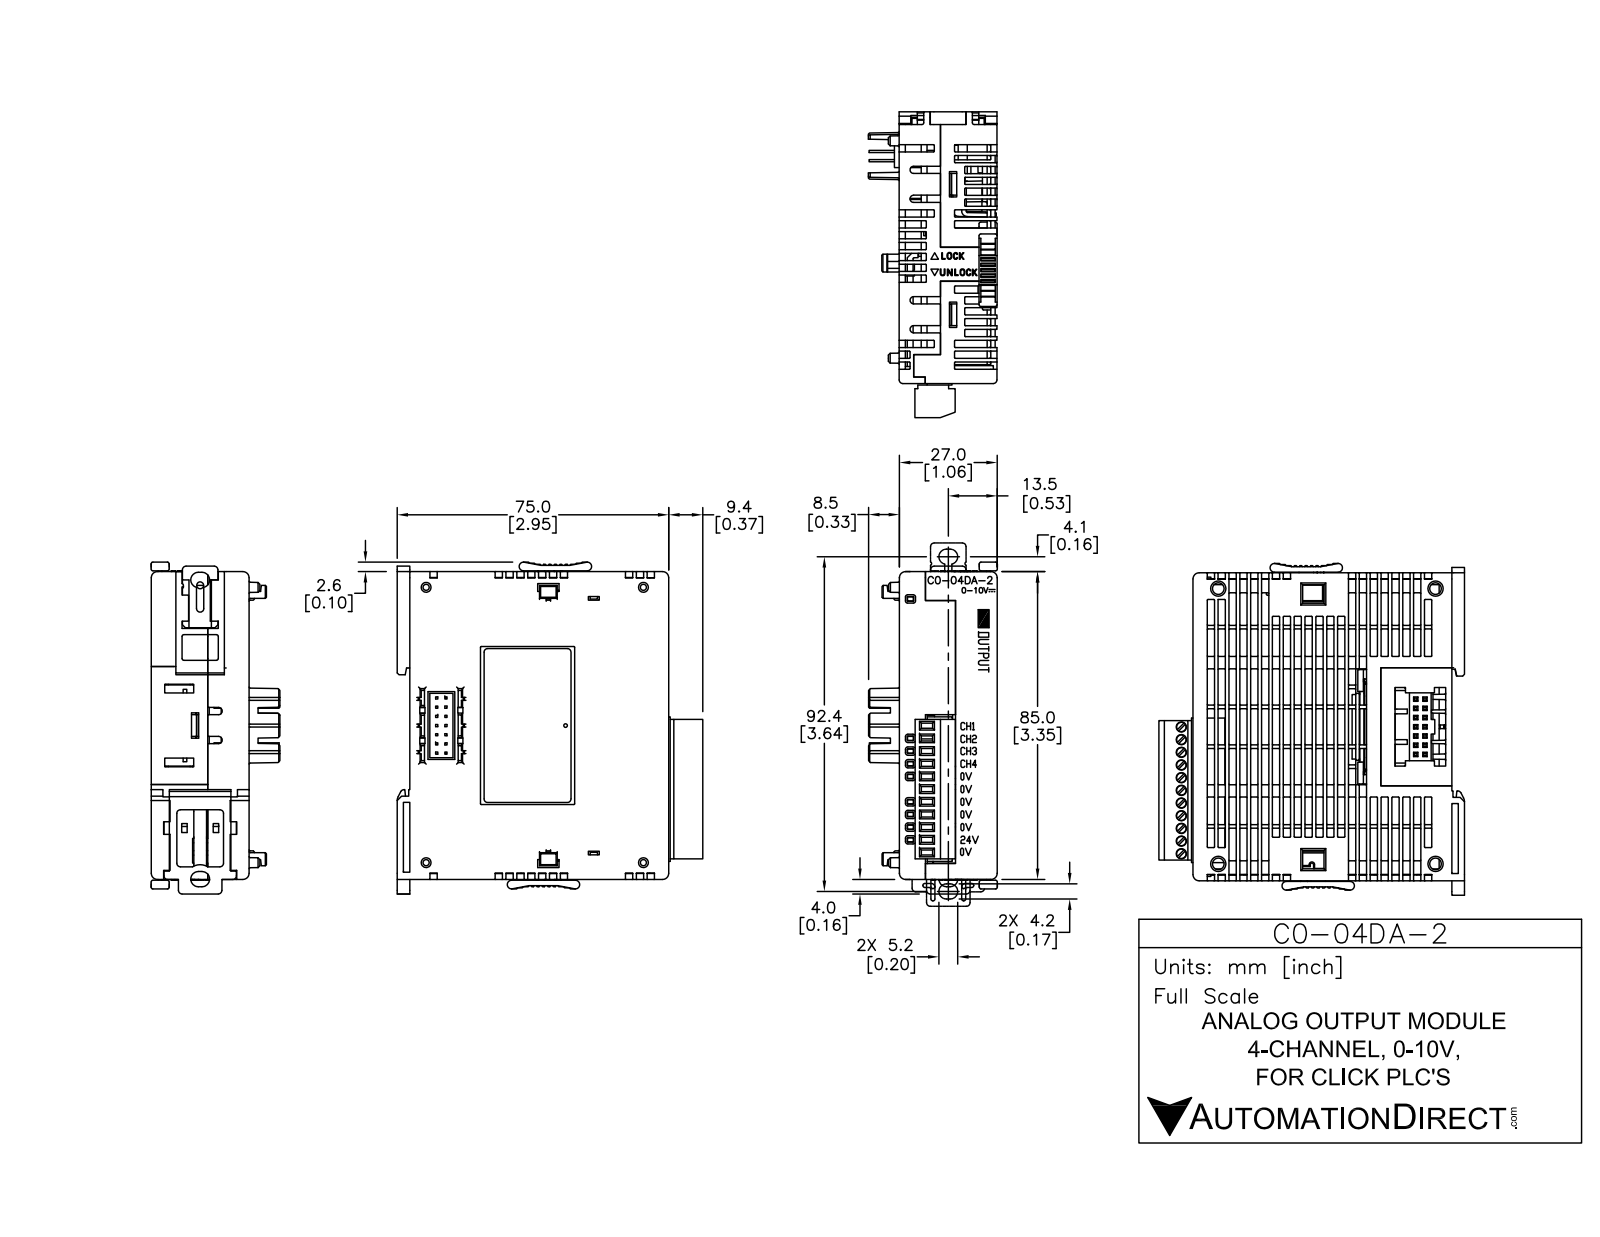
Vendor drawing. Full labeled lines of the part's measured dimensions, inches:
Part name (STEP PRODUCT): C0-04DA-2
STEP written by: SolidWorks 2013 (AUTOMOTIVE_DESIGN)
Units: inches
Bodies: 1 solid, 3792 faces (2700 planar, 968 cylindrical, 124 other)
Overall size (bounding box): 3.606 × 3.323 × 1.4
Volume: 9.917 in³ · Surface area: 49.28 in²
Round holes (diameter × count): ⌀0.039 ×11, ⌀0.11 ×11, ⌀0.126 ×4, ⌀0.079 ×2
Round bosses / shafts (diameter × count): ⌀0.102 ×11, ⌀0.075 ×1
Partial cylindrical surfaces — rounded edges, fillets, slot ends (radius × count): R0.008 ×570, R0.02 ×43, R0.012 ×22, R0.039 ×18, R0.047 ×12, R0.11 ×11, R0.067 ×6, R0.083 ×4
Main face-to-face distances: 1.063, 0.02, 0.02, 1.043, 2.815, 0.067, 3.346, 1.035, 1.056, 3.327
Hole centre spacings: 0.138, 0.276, 0.413, 0.551, 0.689, 0.827, 0.965, 1.102
